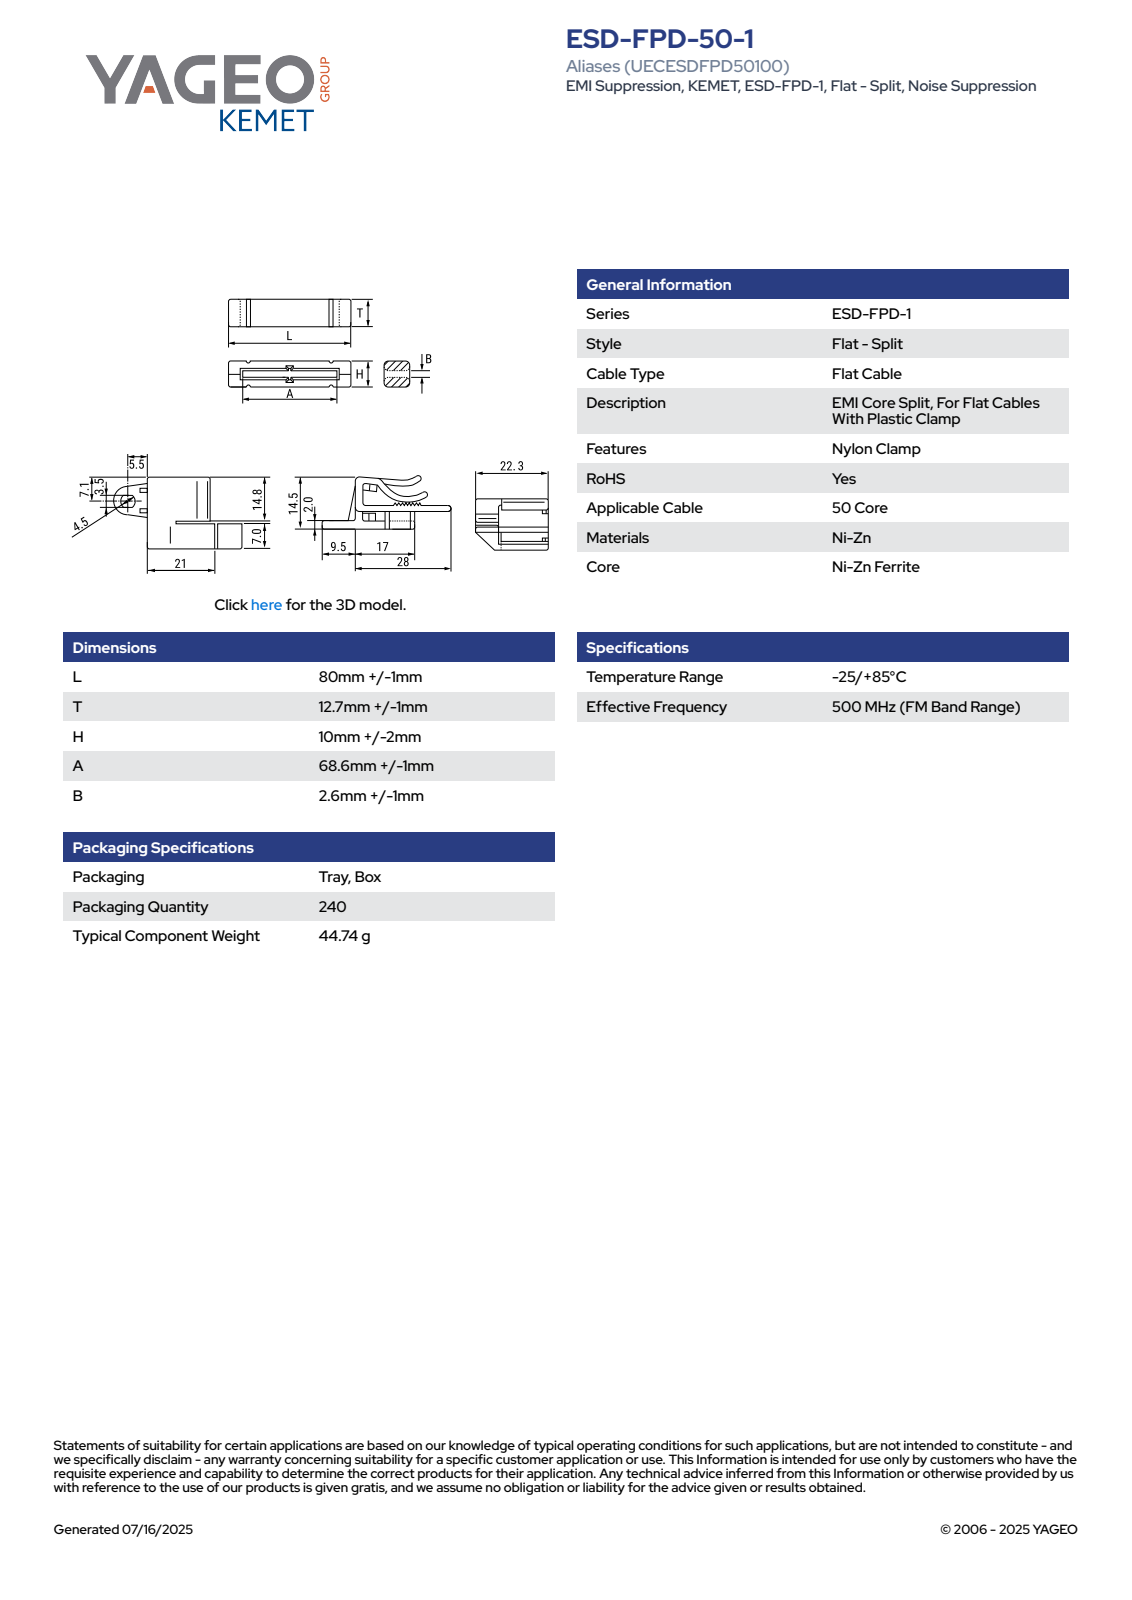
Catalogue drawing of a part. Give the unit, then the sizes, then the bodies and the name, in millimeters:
Units: millimetres
Overall size (bounding box): 81 × 12.7 × 12
Partial cylindrical surfaces — rounded edges, fillets, slot ends (radius × count): R0.5 ×8, R0.62 ×4
Main face-to-face distances: 4.7, 7.3, 12, 2.6, 12.7, 81, 16.76, 6.2, 74.8, 68.6
Volume: 10 007 mm³ · Surface area: 5 651 mm²
Bodies: 4 solids, 91 faces (79 planar, 12 cylindrical, 0 other)
Part name (STEP PRODUCT): EC_FPD1_L81T13.7H12A68.6B2.6
STEP written by: SolidWorks 2021 (AUTOMOTIVE_DESIGN)
